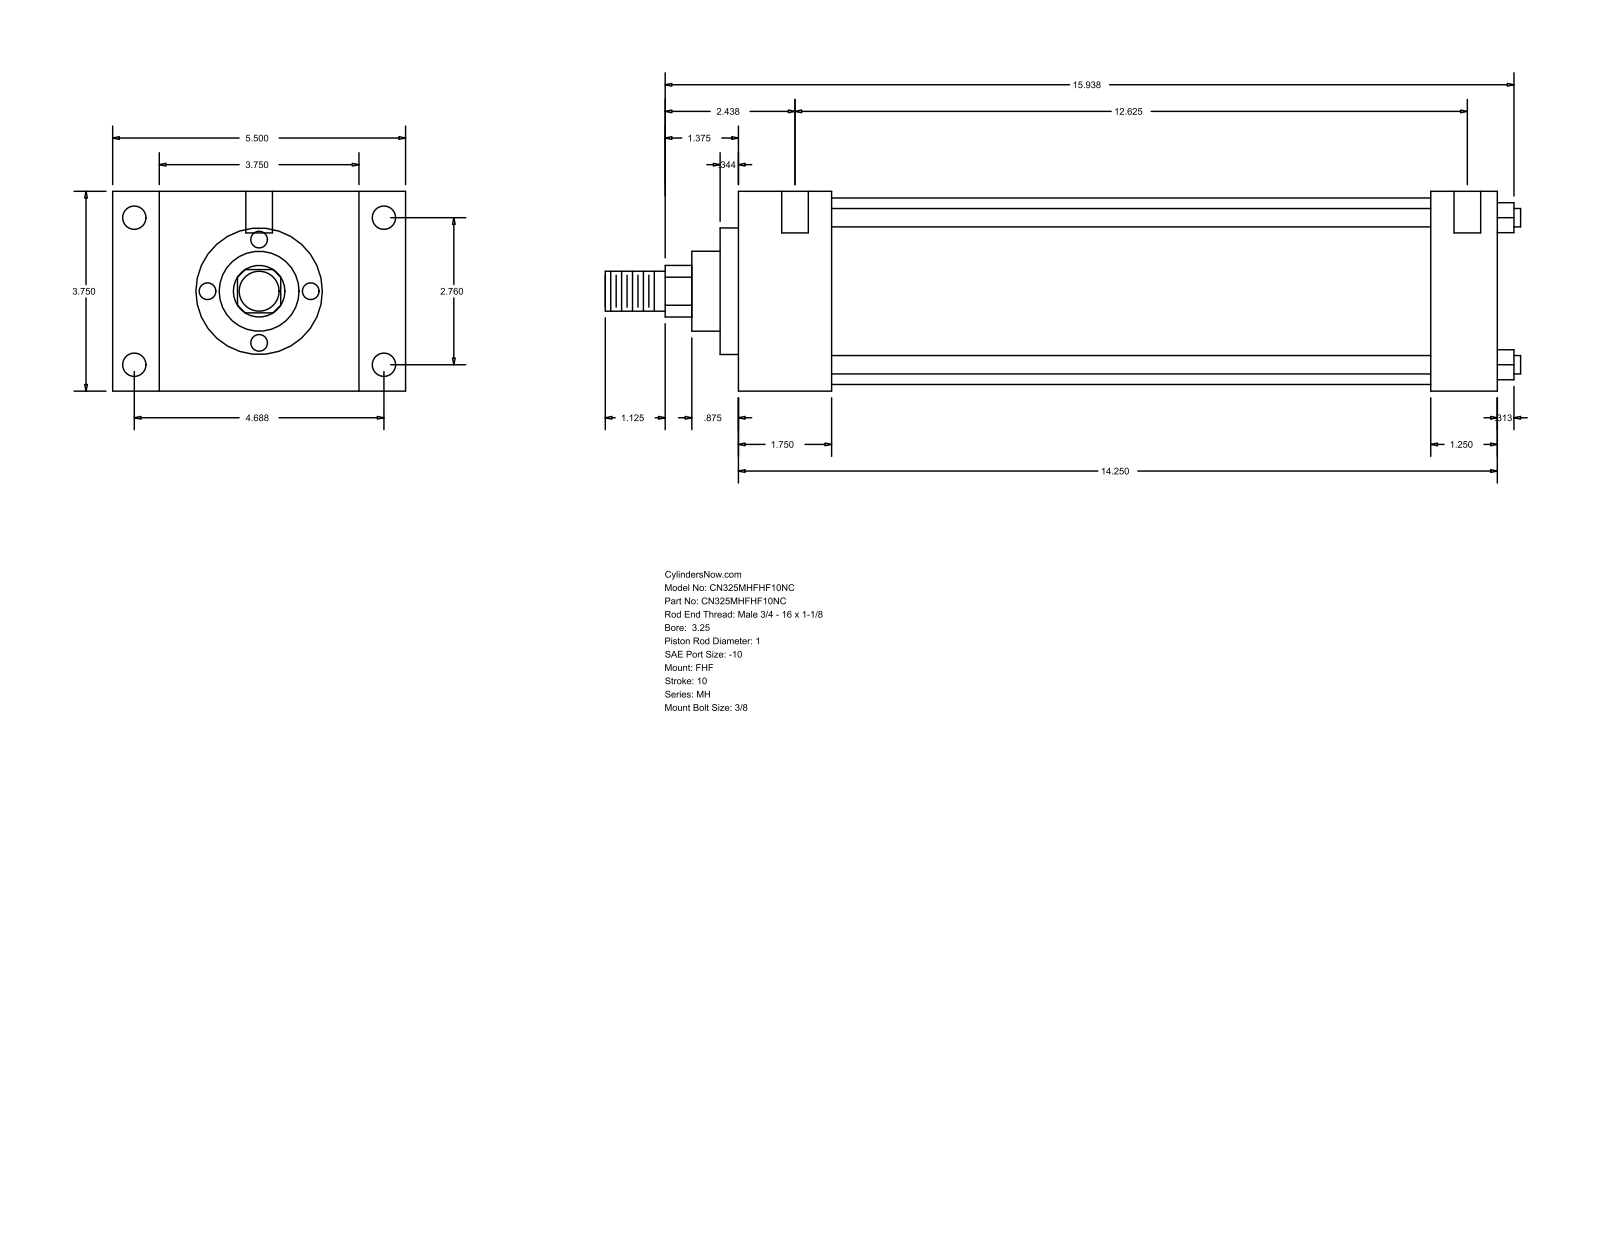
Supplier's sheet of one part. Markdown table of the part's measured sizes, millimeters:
| quantity | value |
| --- | --- |
| part name | MH_FHF__0325_1 |
| STEP written by | GSSL Pune (CONFIG_CONTROL_DESIGN) |
| units | millimeters |
| bodies | 0 solids, 90 faces (61 planar, 29 cylindrical, 0 other) |
| overall size | 436.56 × 139.7 × 95.25 |
| round holes (diameter × count) | 5.56 × 4, 11.13 × 4, 12.7 × 2 |
| round bosses / shafts (diameter × count) | 8.76 × 4, 88.9 × 1, 60.33 × 1, 38.1 × 1, 25.4 × 1, 19.05 × 1 |
| partial cylindrical surfaces (radius × count) | 12.29 × 1 |
| main face-to-face distances | 95.24, 361.96, 44.46, 317.5, 22.23, 117.47, 139.7, 330.2, 285.74, 31.76 |
| hole center spacings | 70.1, 119.06, 138.16, 327.02, 1.58, 4.76, 320.68, 322.26 |
